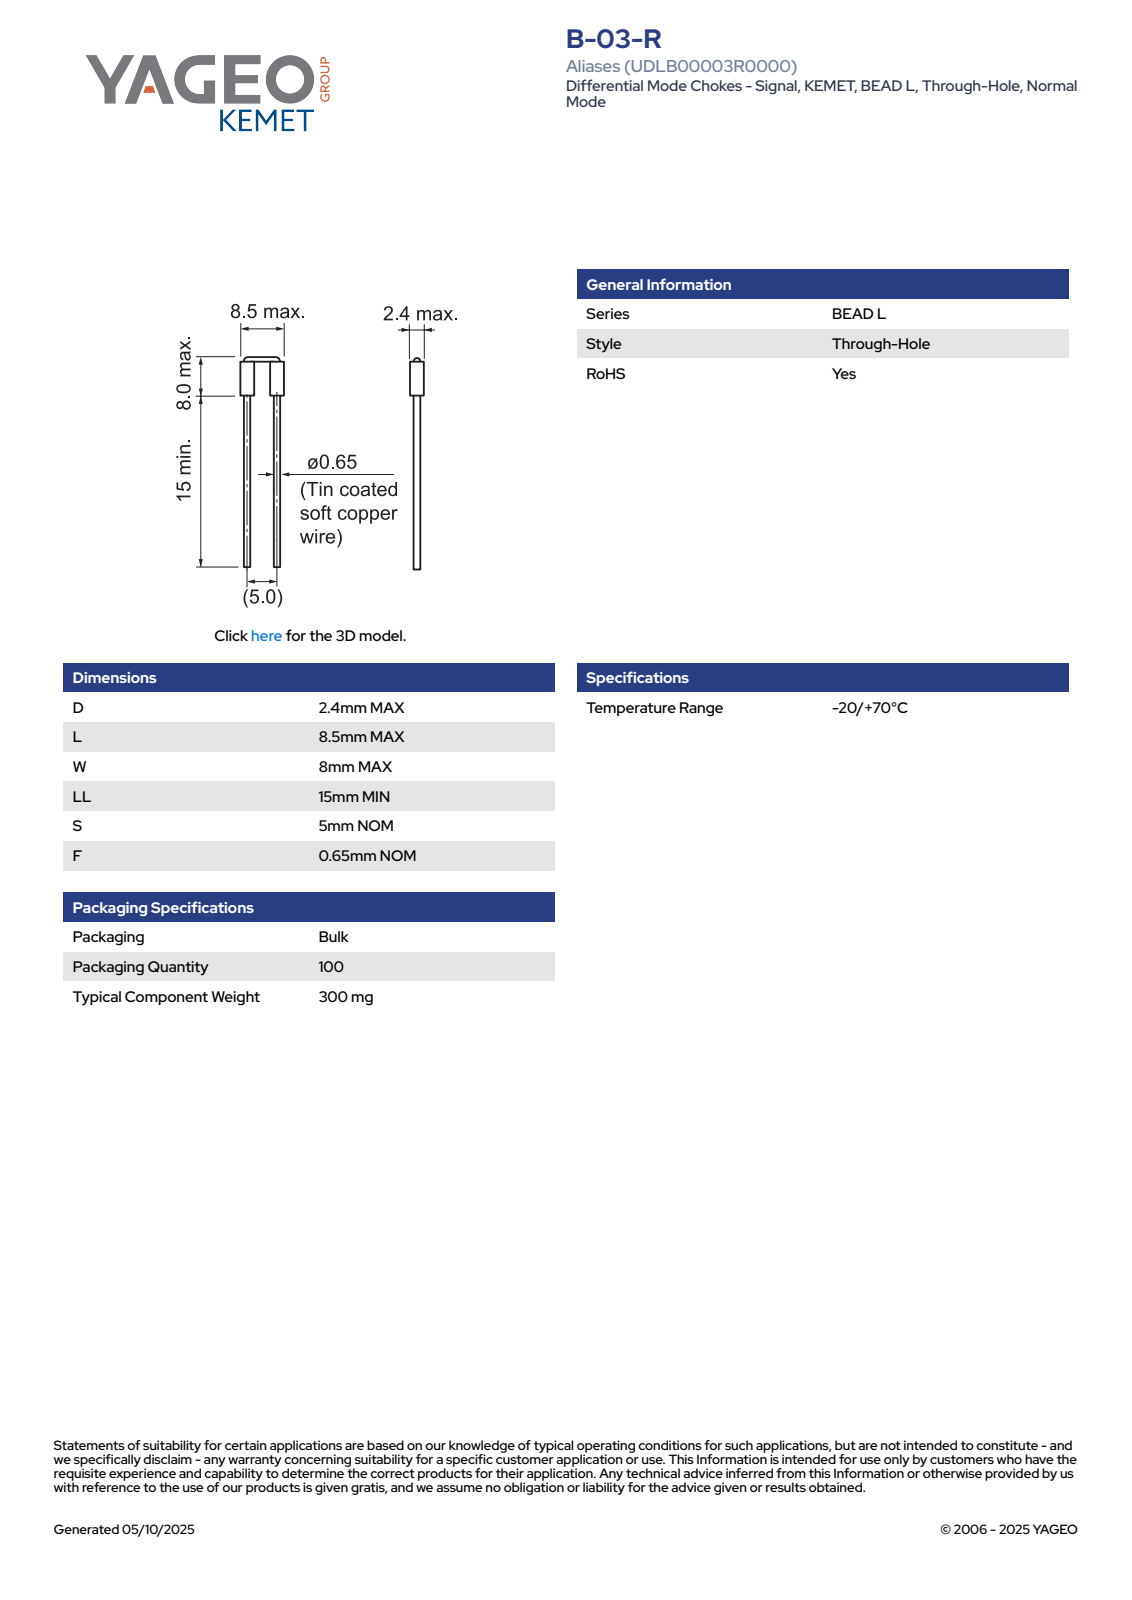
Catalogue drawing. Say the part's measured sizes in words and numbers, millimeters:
The part is named "IL_B03R_D2.4L8.5W8S5LL15". Its 3-D file was written by "SolidWorks 2014 (AUTOMOTIVE_DESIGN)". It is 2 solids with 145 faces: 51 planar, 28 cylindrical and 66 other. Overall it measures 23 by 8.5 by 2.41 millimeters. Its volume is 78 cubic millimeters and its surface area 202 square millimeters. Round bosses or shafts: 3 of diameter 0.65, 2 of diameter 2.4. Partial cylindrical surfaces (rounded edges, fillets, slot ends): 2 of radius 1.21. The main face-to-face distances are 7.35, 15, 22.35, 5.76, 5.97, 6.08, 6.09.
